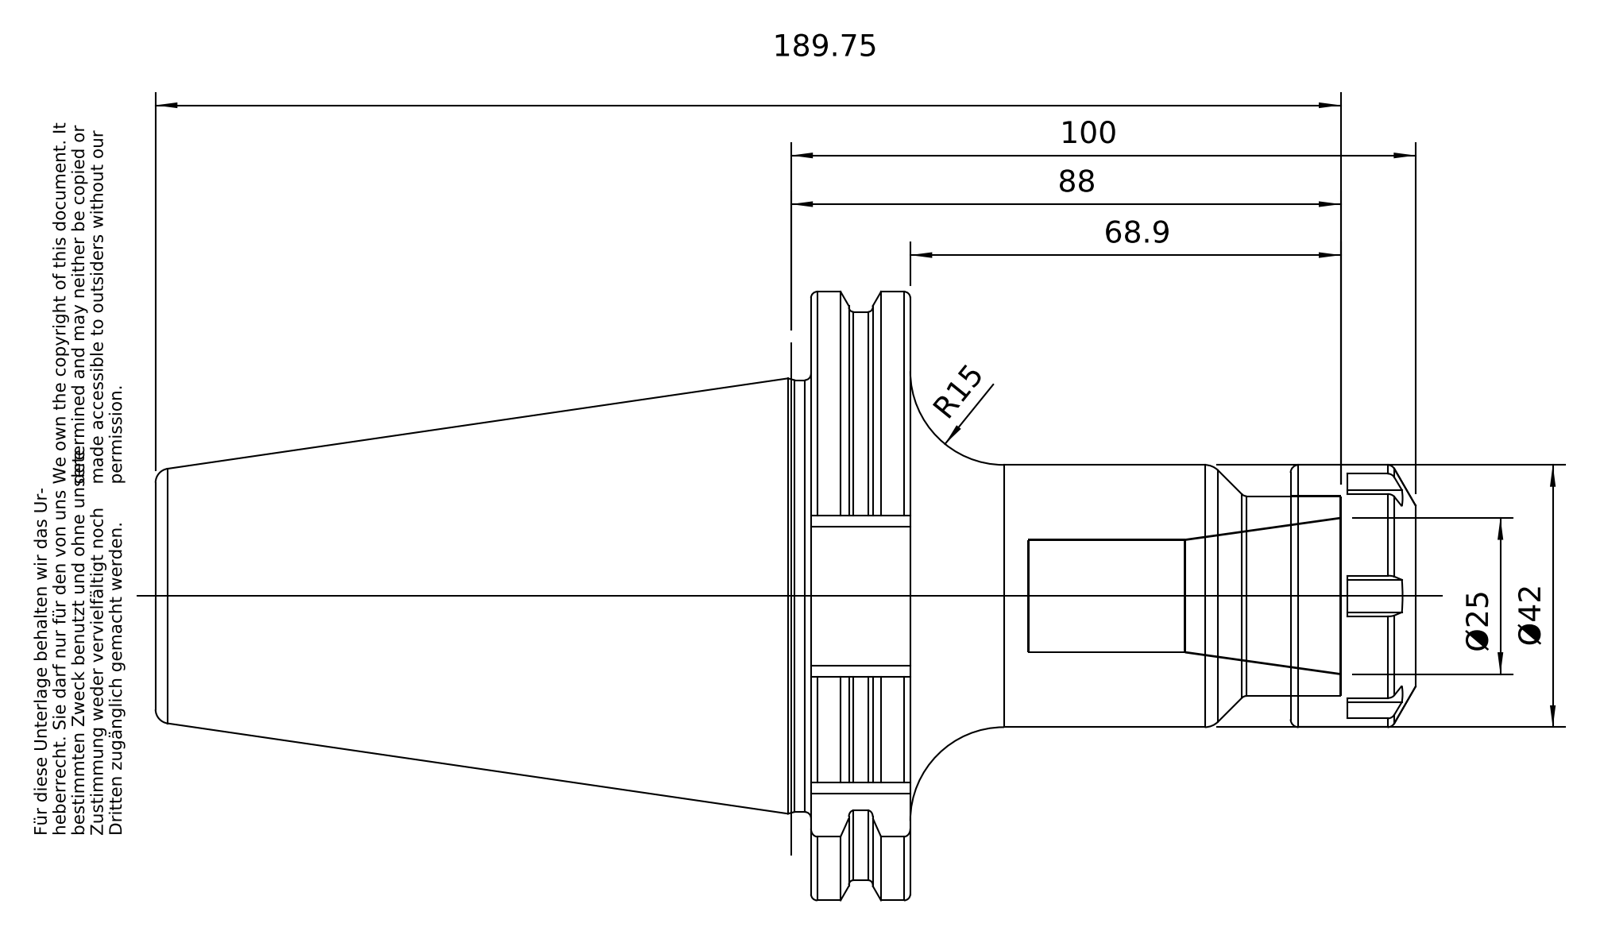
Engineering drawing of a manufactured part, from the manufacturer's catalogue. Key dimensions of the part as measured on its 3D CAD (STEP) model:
Part name (STEP PRODUCT): 50-321-25; 83-912-25; 50-321-25_ASM
STEP written by: PRO/ENGINEER BY PARAMETRIC TECHNOLOGY CORPORATION, 2010430 (CONFIG_CONTROL_DESIGN)
Units: millimetres
Bodies: 2 solids, 147 faces (41 planar, 32 cylindrical, 74 other)
Overall size (bounding box): 201.6 × 97.47 × 94
Volume: 441 901 mm³ · Surface area: 58 055 mm²
Round holes (diameter × count): ⌀18 ×1, ⌀20.75 ×1, ⌀25.01 ×1, ⌀25.7 ×1
Round bosses / shafts (diameter × count): ⌀91 ×1, ⌀69.15 ×1, ⌀42 ×1, ⌀32 ×1, ⌀24.01 ×1
Partial cylindrical surfaces — rounded edges, fillets, slot ends (radius × count): R1.75 ×5, R48.74 ×1
Main face-to-face distances: 15.85, 76.8, 60.95, 96.8, 80.95, 20, 104.8, 120.65, 181.6, 201.6
